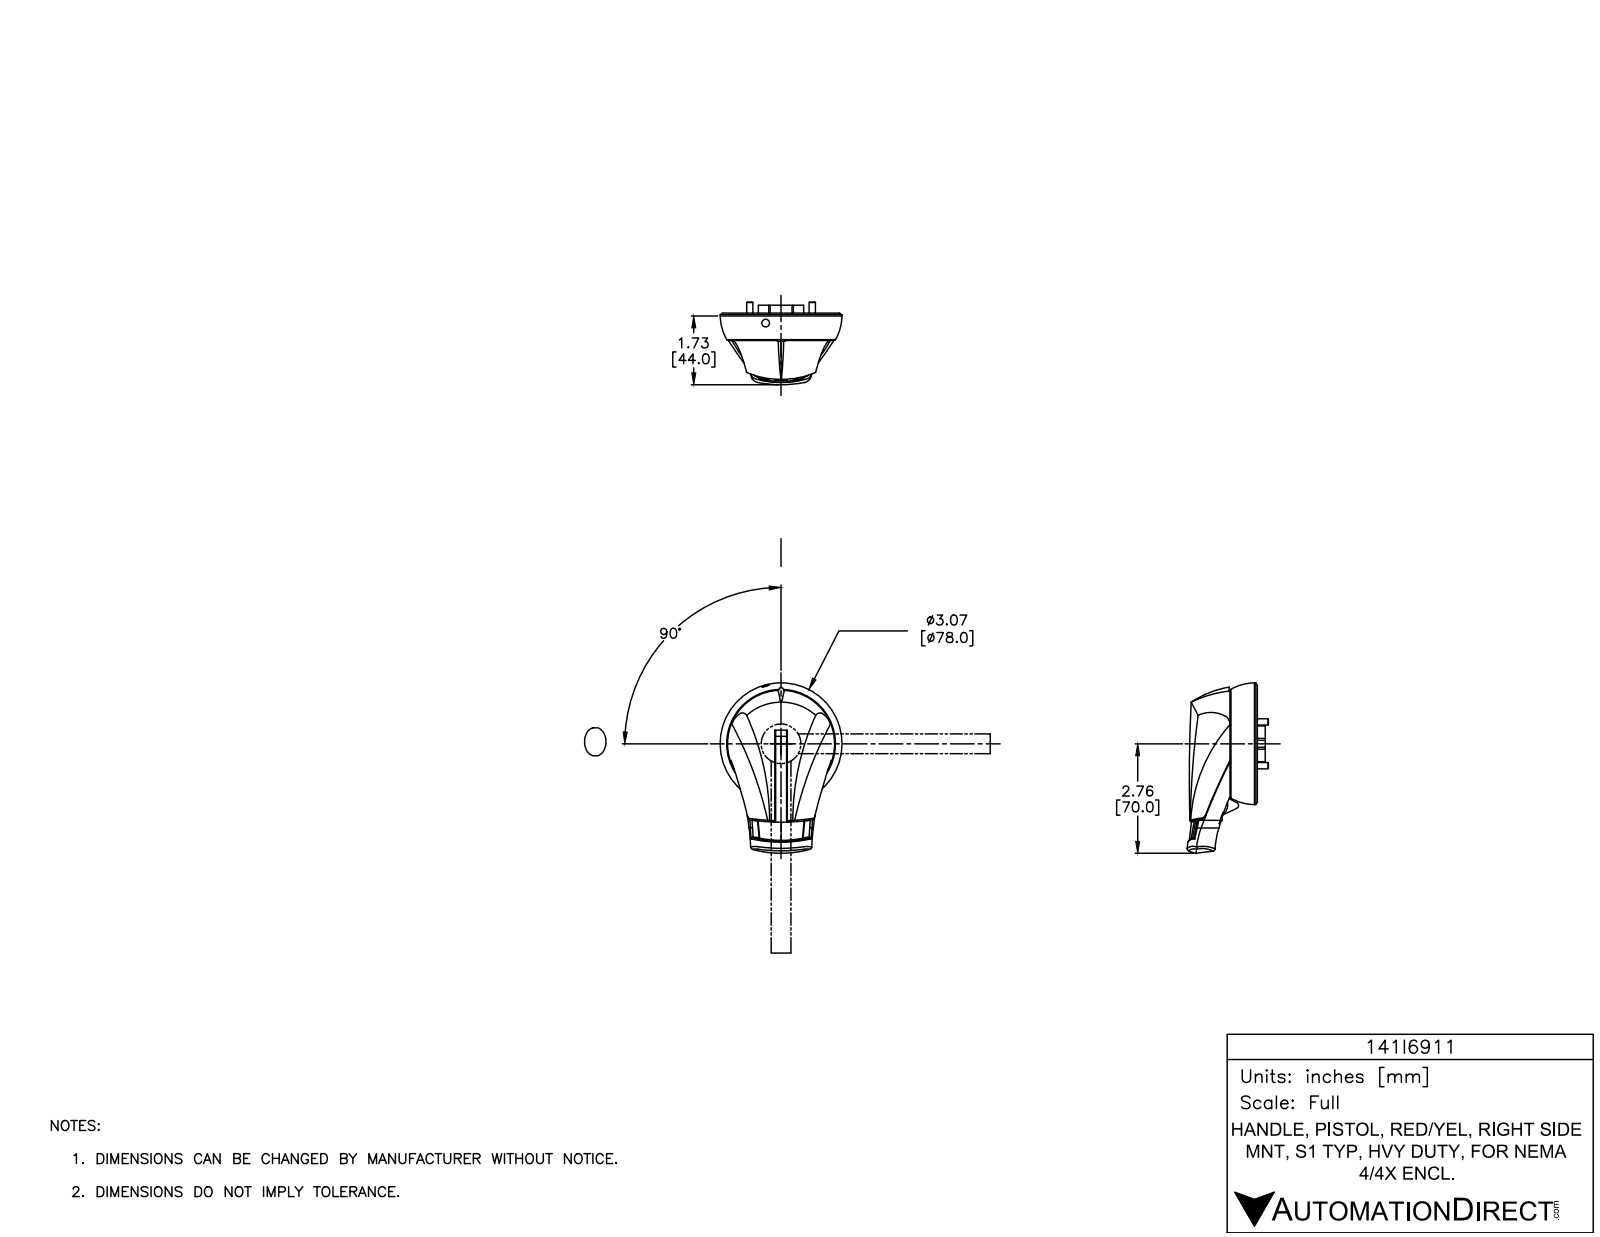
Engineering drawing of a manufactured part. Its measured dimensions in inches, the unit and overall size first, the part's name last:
Units: inches
Overall size (bounding box): 4.291 × 3.07 × 2.046
Round holes (diameter × count): ⌀0.157 ×6, ⌀0.339 ×4, ⌀0.425 ×4, ⌀0.03 ×3, ⌀0.169 ×2, ⌀0.362 ×2, ⌀0.118 ×1, ⌀0.189 ×1, ⌀2.992 ×1
Round bosses / shafts (diameter × count): ⌀0.02 ×11, ⌀0.335 ×4, ⌀0.315 ×4, ⌀0.089 ×3, ⌀0.069 ×3, ⌀0.228 ×2, ⌀2.819 ×1, ⌀2.701 ×1
Partial cylindrical surfaces — rounded edges, fillets, slot ends (radius × count): R0.01 ×221, R0.015 ×20, R0.034 ×20, R0.03 ×15, R0.039 ×4, R0.025 ×3, R5.437 ×3, R0.079 ×2
Main face-to-face distances: 0.024, 0.701, 0.713, 0.689, 0.035, 0.102, 0.276, 0.173, 0.244, 0.047
Hole centre spacings: 0.961, 0.309, 0.669, 1.098, 1.102, 1.203, 1.575, 1.881
Volume: 7.72 in³ · Surface area: 79.65 in²
Bodies: 8 solids, 1516 faces (810 planar, 548 cylindrical, 158 other)
Part name (STEP PRODUCT): 141I6911
STEP written by: SolidWorks 2015 (AUTOMOTIVE_DESIGN)
